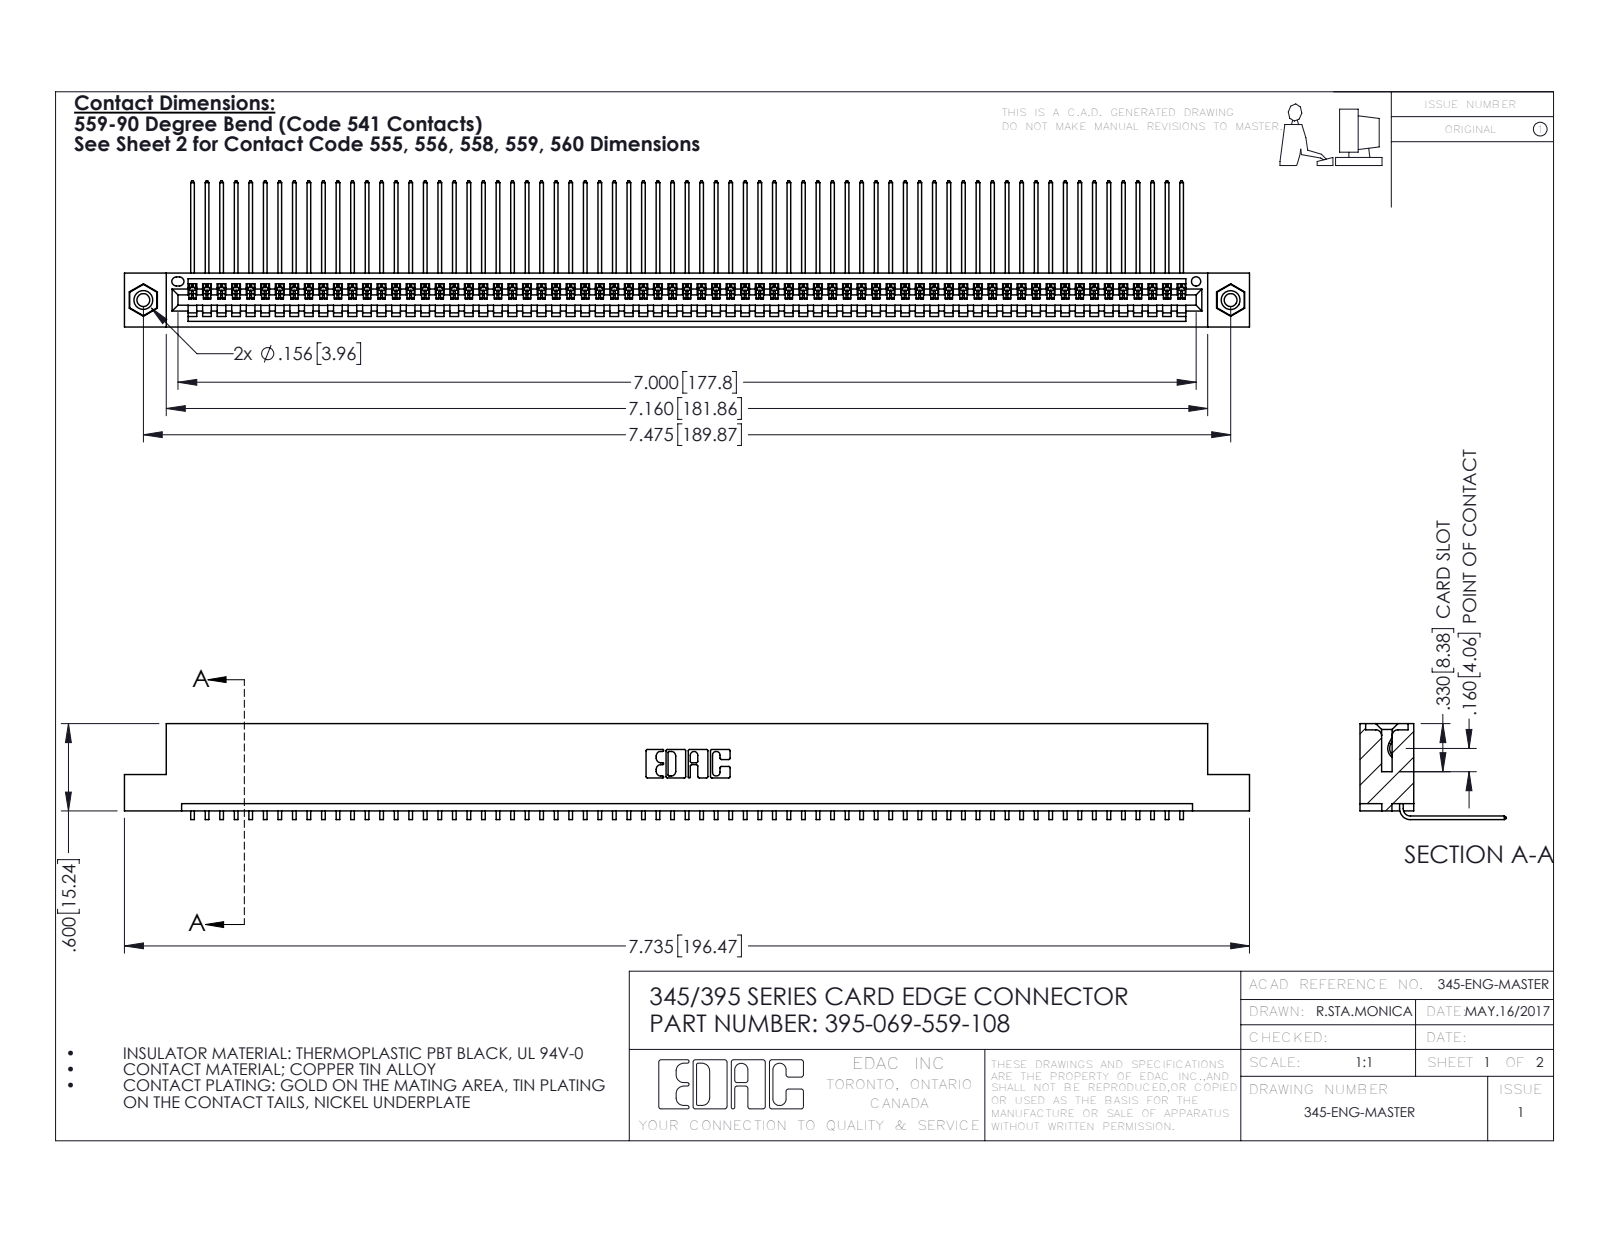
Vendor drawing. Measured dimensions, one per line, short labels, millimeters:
name: 345-292-001_558 559 Tail - 1; 345-250-001_345-250-003-102; 345 Part_Flush Mounting Lugs - 0.156 Dia-TI; 395-069-559-108
written by: SolidWorks 2016 (CONFIG_CONTROL_DESIGN)
unit: mm
bodies: 72 solids, 4326 faces (3010 planar, 1300 cylindrical, 16 other)
size: 196.5 × 25.5 × 16.7
volume: 19 110 mm³; area: 27 130 mm²
holes: 2× ⌀2.3, 2× ⌀3.2, 2× ⌀4, 1× ⌀1.6
bosses: 2× ⌀3.9
rounds: 138× R0.2, 22× R0.3, 6× R0.2, 6× R0.8, 3× R0.7, 2× R0.8, 2× R1, 1× R0.4
face distances: 1.8, 7.6, 9.4, 5.1, 2.5, 6.9, 0.6, 5.7, 3.8, 1.8
hole spacings: 6.9, 183.9, 189.9
